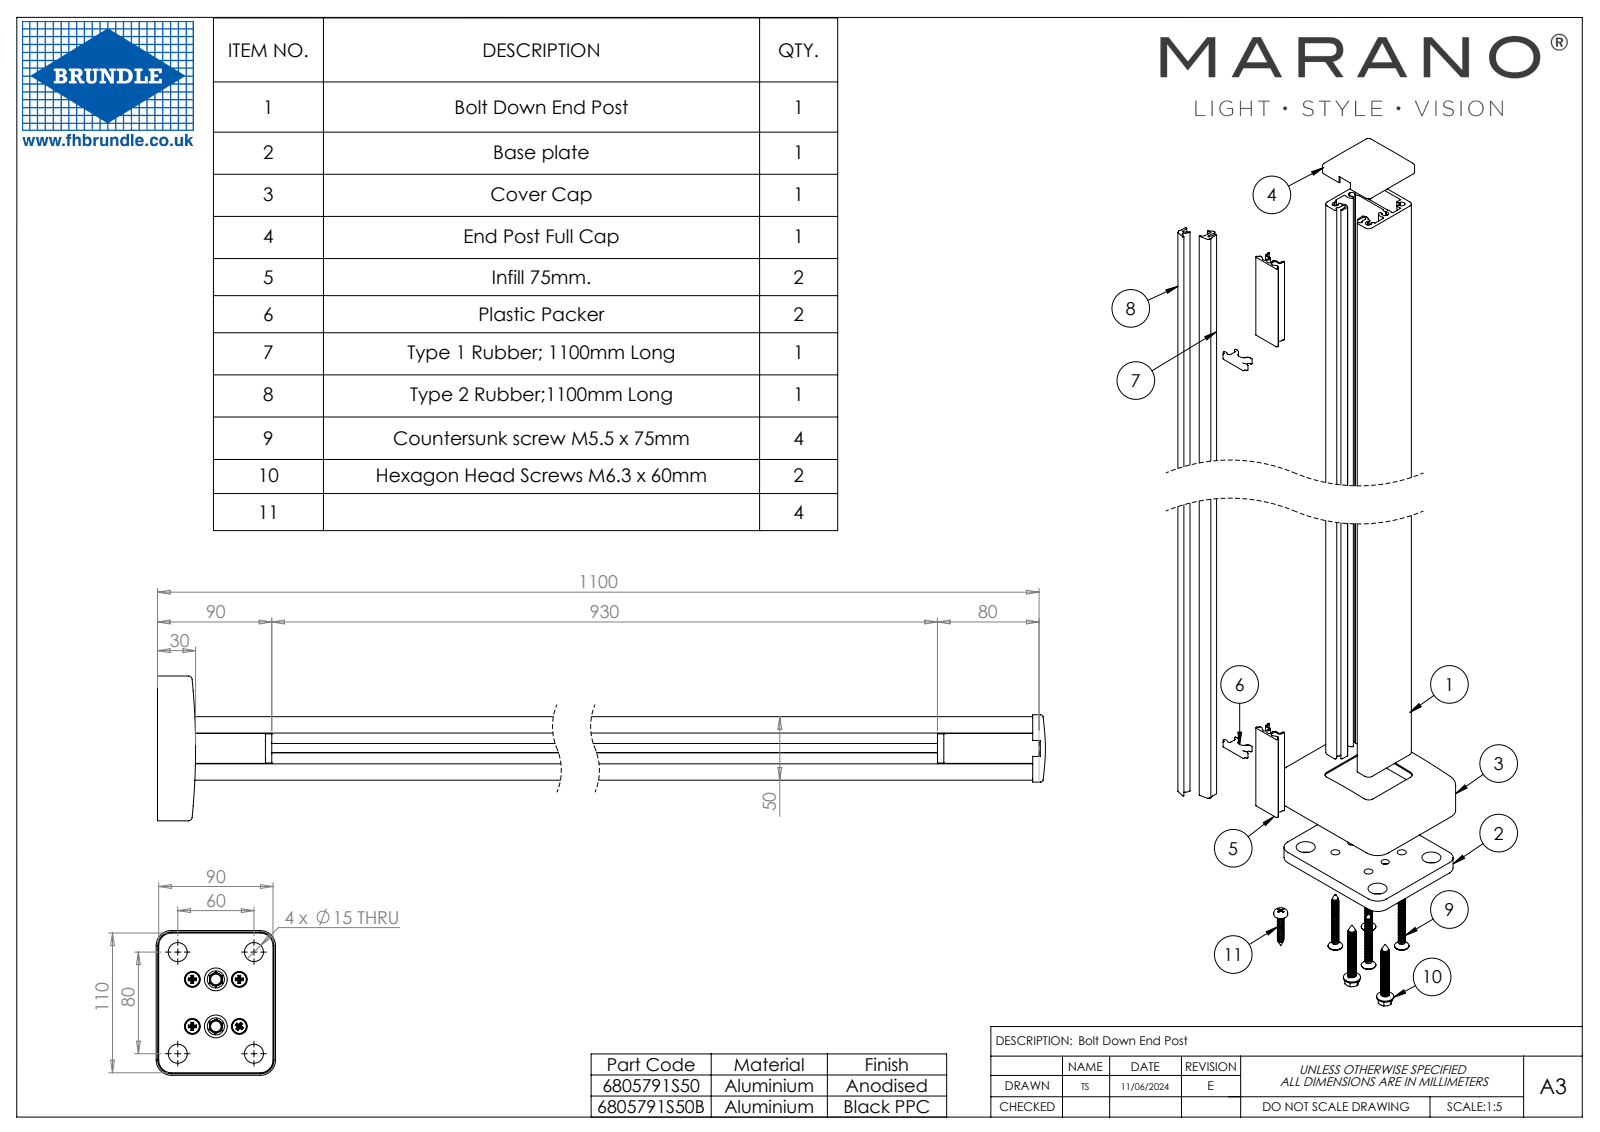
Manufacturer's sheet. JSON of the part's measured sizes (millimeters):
{"part_name": "680579 Part3_930mm; 68PP01; 6805791S50 Part1; 680520850 (+7 more)", "step_written_by": "SolidWorks 2020 (CONFIG_CONTROL_DESIGN)", "units": "millimeters", "bodies": {"solids": 16, "faces": 2116, "planar": 405, "cylindrical": 915, "other": 796}, "overall_size": [1105, 114, 94], "volume_mm3": 1099000, "surface_area_mm2": 762628, "round_holes": [[7, 4], [12.5, 4], [15, 4], [6.5, 2], [8.33, 2], [18, 2]], "round_bosses_or_shafts": [[11.5, 4], [5.5, 4], [13.5, 2], [6.3, 2]], "partial_cylinders_radius": [[0.5, 117], [1, 27], [3, 13], [2, 10], [0.3, 7], [0.6, 5], [5, 5], [1.5, 4]], "face_to_face_distances": [50, 3, 47, 20.25, 2, 22.25, 19.25, 17.25, 27.75, 29.75], "hole_center_spacings": [37, 18.5, 24.38, 36.91, 41.37, 53.05, 59.62, 65.74]}
